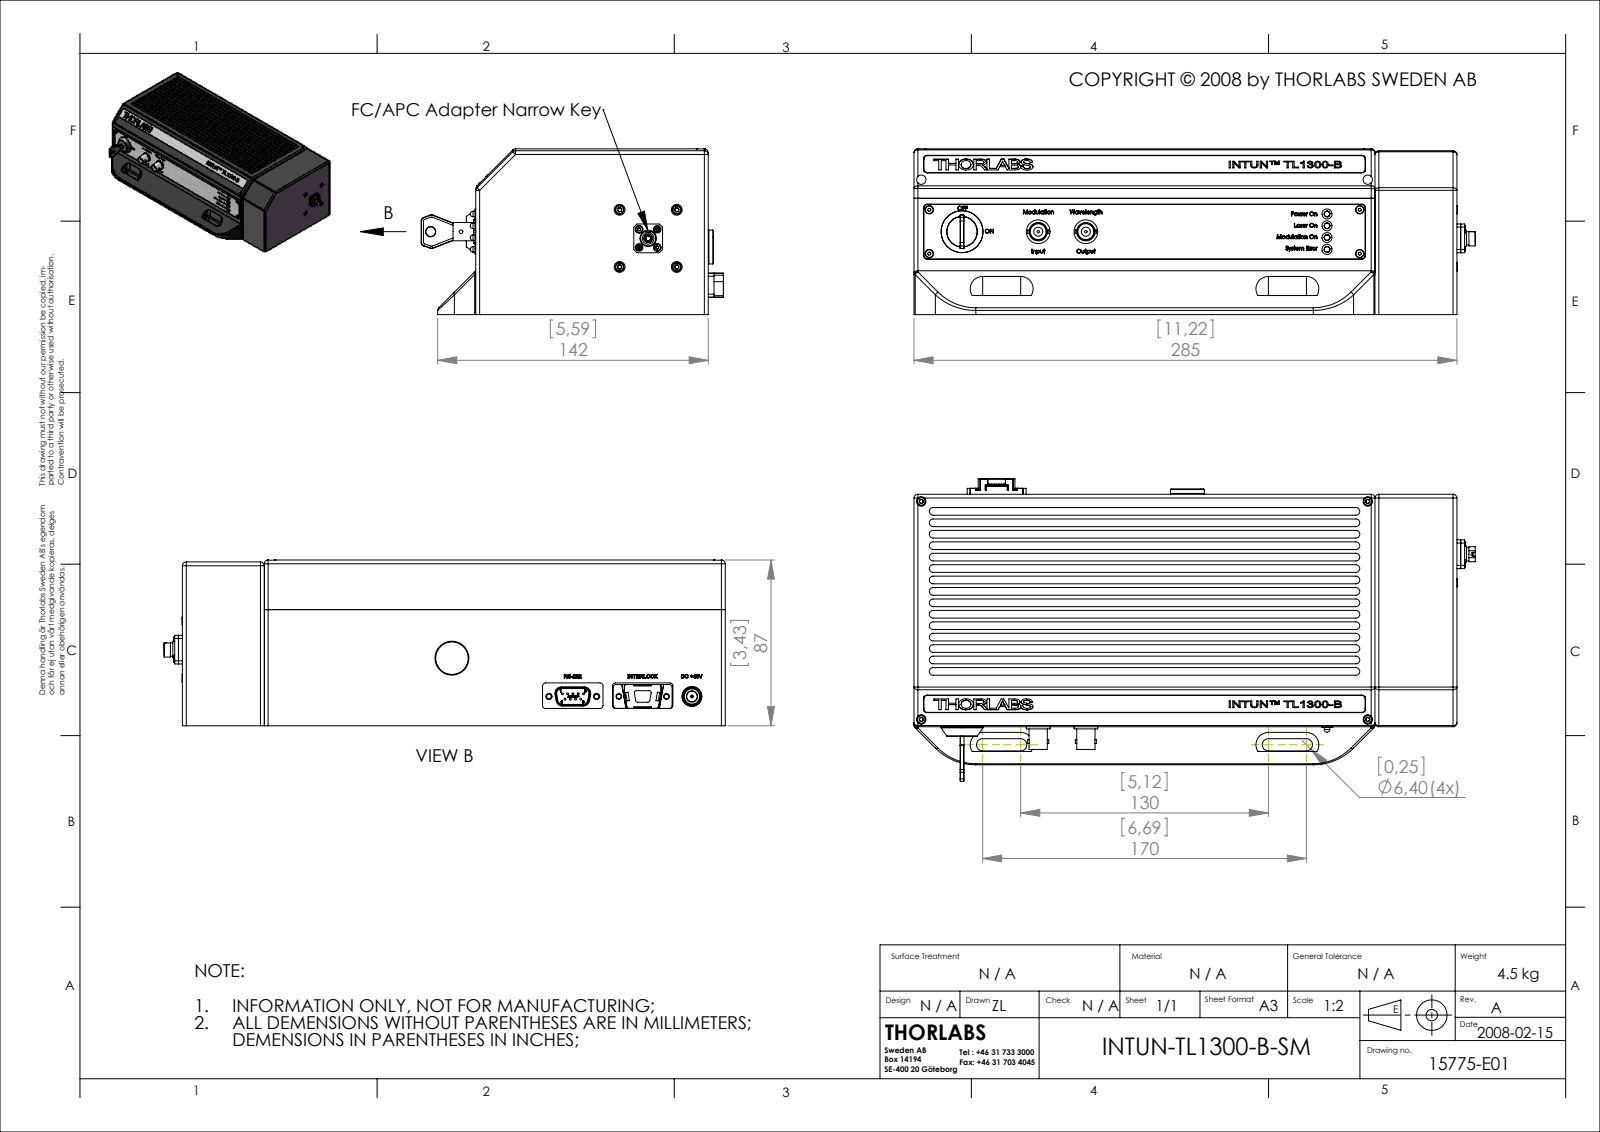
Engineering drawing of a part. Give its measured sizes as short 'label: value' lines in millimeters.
name: INTUN-TL1300-B-SM
written by: SolidWorks 2007 (CONFIG_CONTROL_DESIGN)
unit: mm
bodies: 0 solids, 3674 faces (1985 planar, 777 cylindrical, 912 other)
size: 294.61 × 158.68 × 87
holes: 9× ⌀1.02, 8× ⌀1.6, 7× ⌀2.05, 4× ⌀2.22, 4× ⌀2.26, 4× ⌀2.4, 4× ⌀2.5, 4× ⌀2.9, 4× ⌀3, 4× ⌀3.05, 4× ⌀3.2, 4× ⌀3.99
bosses: 9× ⌀4.5, 9× ⌀2.5, 9× ⌀1.02, 6× ⌀2, 4× ⌀6.2, 4× ⌀5.3, 4× ⌀4.7, 4× ⌀4.25
rounds: 79× R2, 18× R5, 16× R1.57, 14× R0.2, 10× R1.02, 10× R3.5, 10× R6, 9× R0.71
face distances: 6, 2, 5.6, 6.25, 77.75, 72.15, 116, 1, 83, 77.4
hole spacings: 9.51, 22.25, 22.26, 2.77, 23, 6.72, 6.73, 9.5
